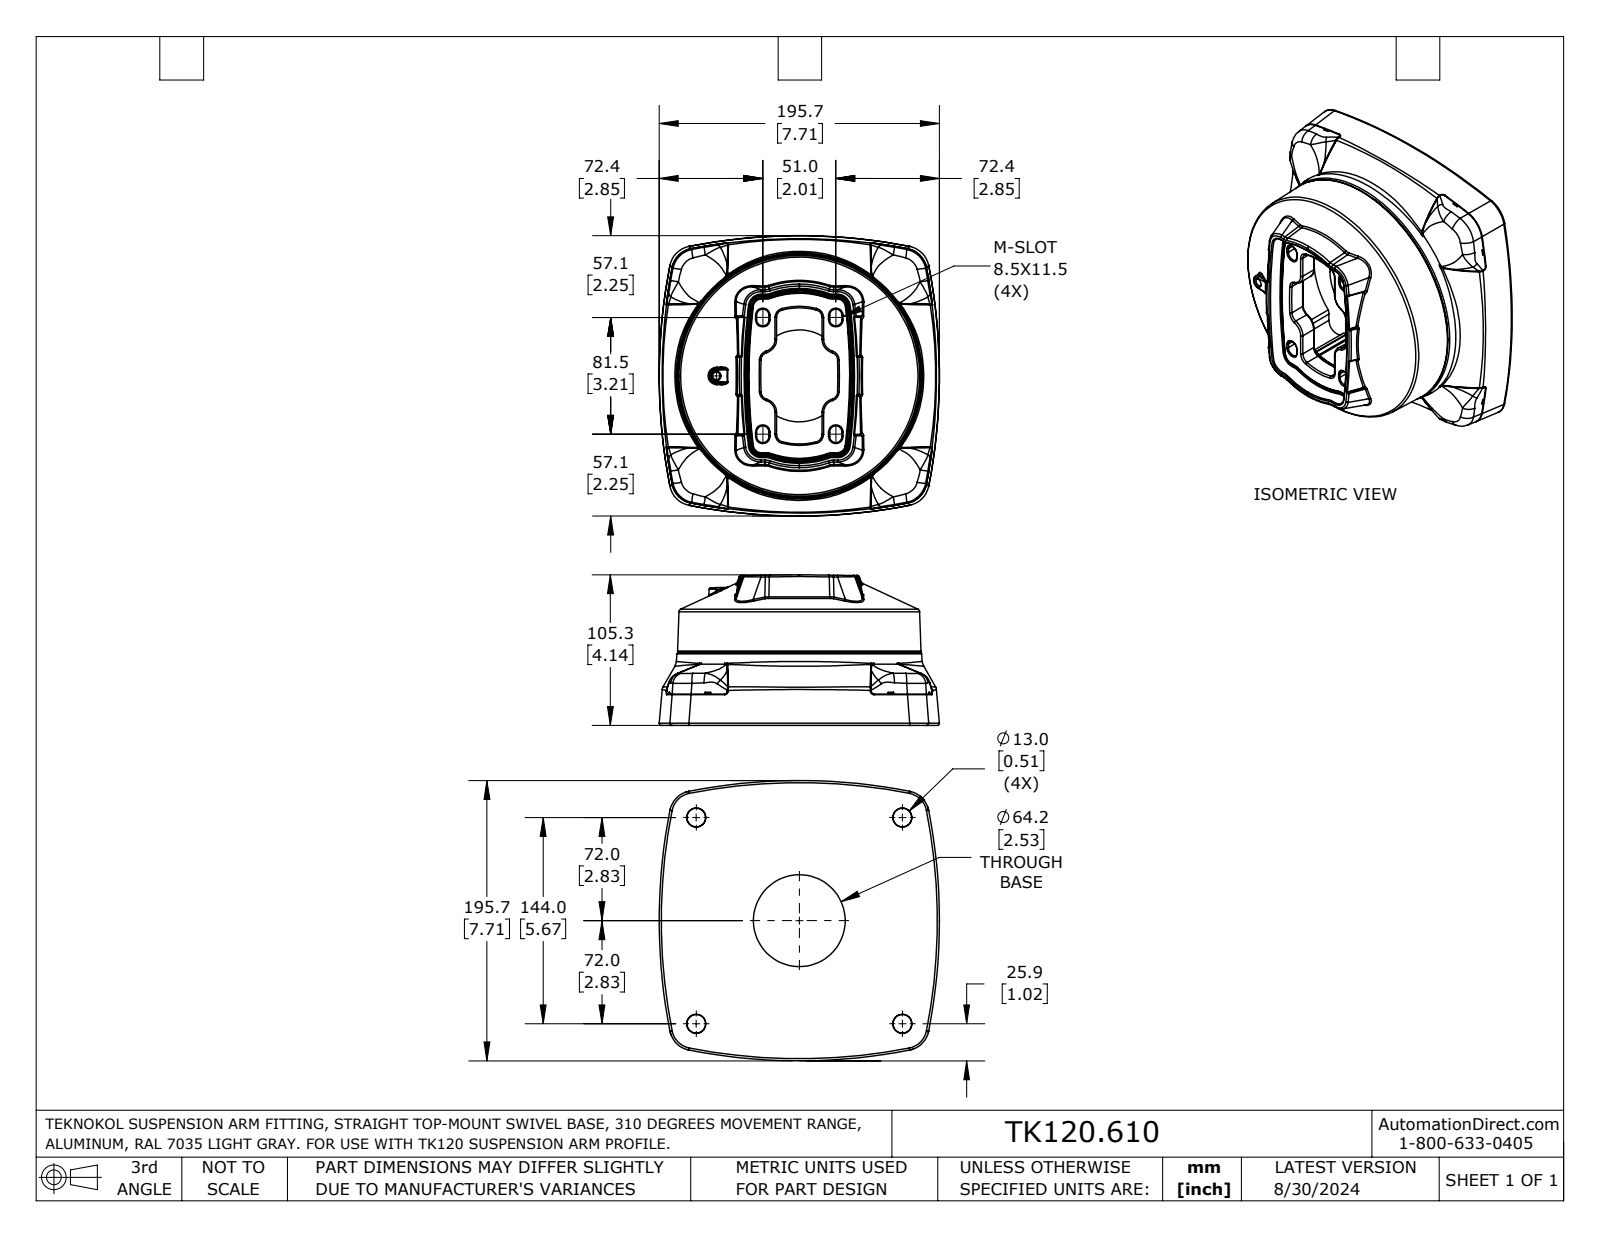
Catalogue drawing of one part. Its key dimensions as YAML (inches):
part_name: "TK120.610"
step_written_by: "SolidWorks 2023 (AUTOMOTIVE_DESIGN)"
units: inches
bodies: {solids: 1, faces: 1003, planar: 130, cylindrical: 87, other: 786}
overall_size: [7.706, 7.705, 4.196]
volume: 119.8
surface_area: 281.4
round_holes:
  - {diameter: 0.666, count: 3}
  - {diameter: 0.205, count: 1}
  - {diameter: 2.526, count: 1}
round_bosses_or_shafts:
  - {diameter: 0.197, count: 8}
partial_cylinders:
  - {radius: 0.043, count: 14}
  - {radius: 0.03, count: 12}
  - {radius: 0.077, count: 8}
  - {radius: 0.079, count: 8}
  - {radius: 0.02, count: 4}
  - {radius: 0.055, count: 4}
  - {radius: 0.296, count: 4}
  - {radius: 1.877, count: 1}
face_to_face_distances: [2.006, 1.732, 3.738, 0.511, 1.22, 3.226, 0.551, 0.039, 1.181, 3.187]
hole_center_spacings: [4.009, 2.283, 2.887, 2.888, 5.669, 5.669, 5.85, 8.017]
